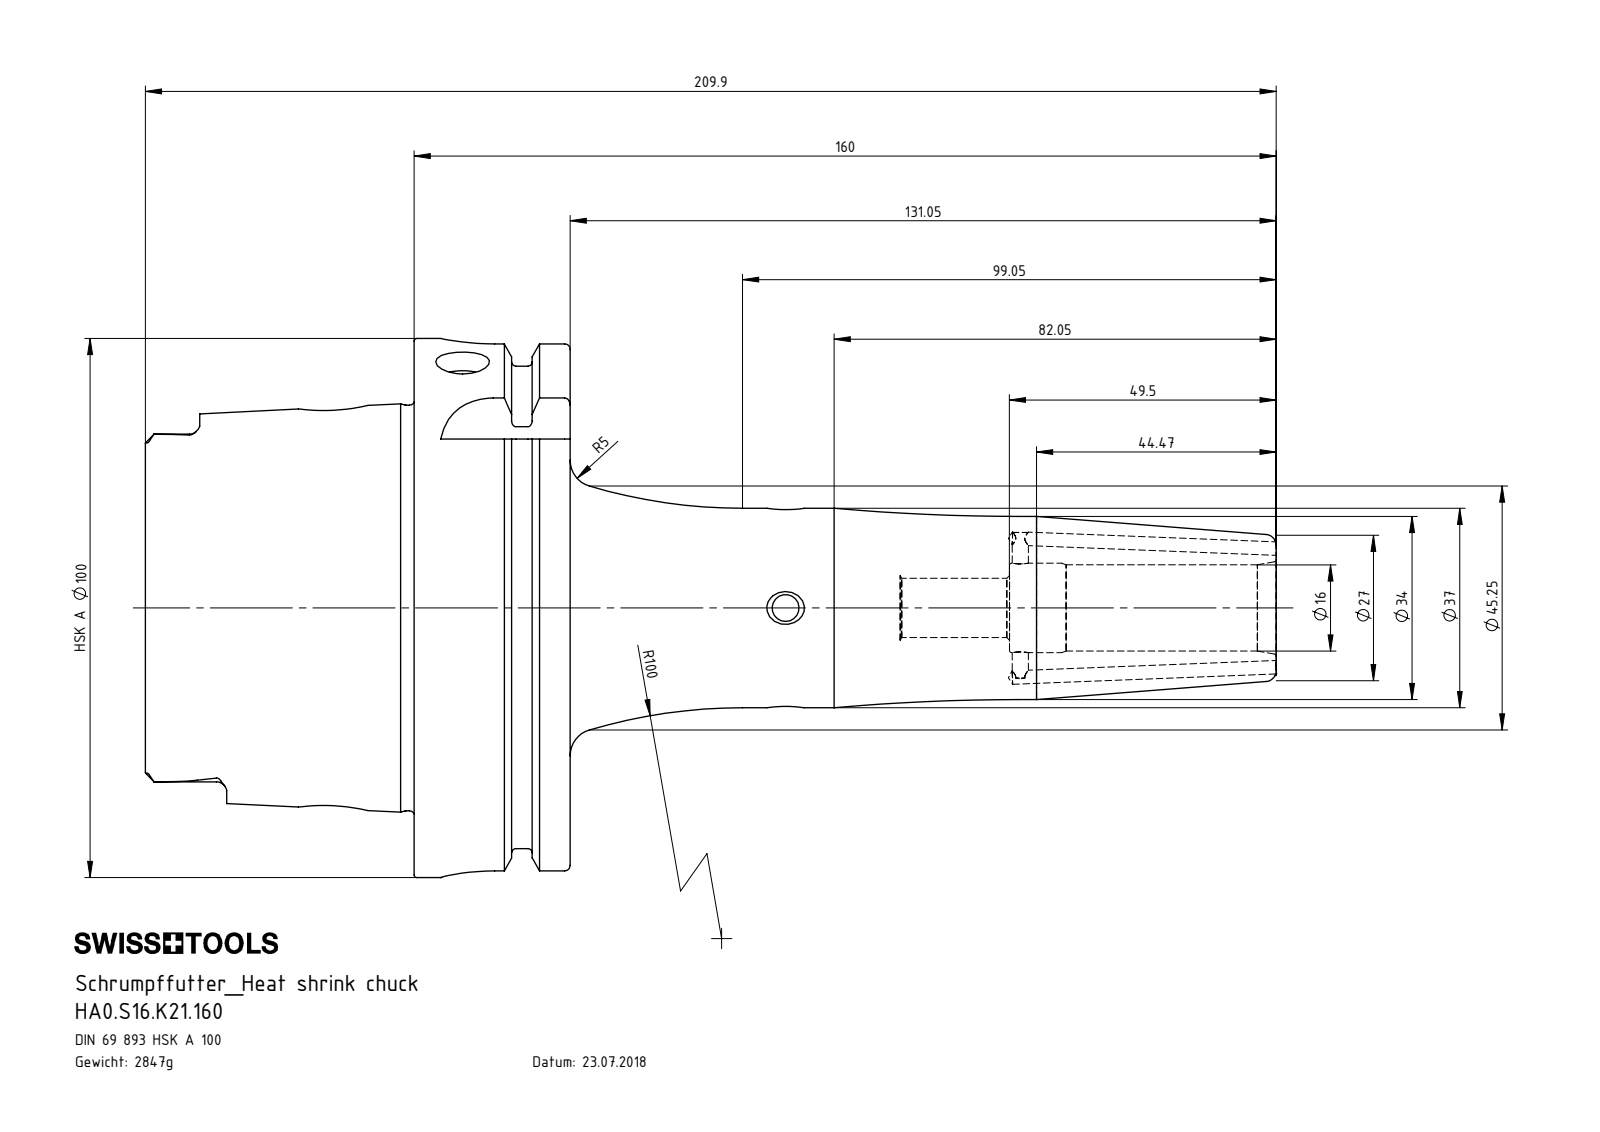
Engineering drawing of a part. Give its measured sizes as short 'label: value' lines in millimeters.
name: HA0.S16.K21.160; ERU-CJ2.001.006; ERU-AN5.K01.020_A; HA0-S16.K21.160_C_Fertigbearbeitung
written by: SolidWorks 2017 (CONFIG_CONTROL_DESIGN)
unit: mm
bodies: 4 solids, 307 faces (95 planar, 89 cylindrical, 123 other)
size: 209.98 × 100 × 100
volume: 362 727 mm³; area: 71 105 mm²
holes: 3× ⌀10, 2× ⌀2.5, 2× ⌀5, 2× ⌀12, 1× ⌀3, 1× ⌀6, 1× ⌀11, 1× ⌀16, 1× ⌀16.6, 1× ⌀22.5, 1× ⌀26, 1× ⌀53
bosses: 2× ⌀3, 1× ⌀100, 1× ⌀91.95, 1× ⌀75.26, 1× ⌀37, 1× ⌀34
rounds: 6× R1.9, 4× R4.88, 4× R10
face distances: 28.95, 12.45, 16.5, 49.9, 62.35, 78.85, 87.8, 78.2, 28.3, 15.85
hole spacings: 43.55, 61.95, 83.95, 127.5
